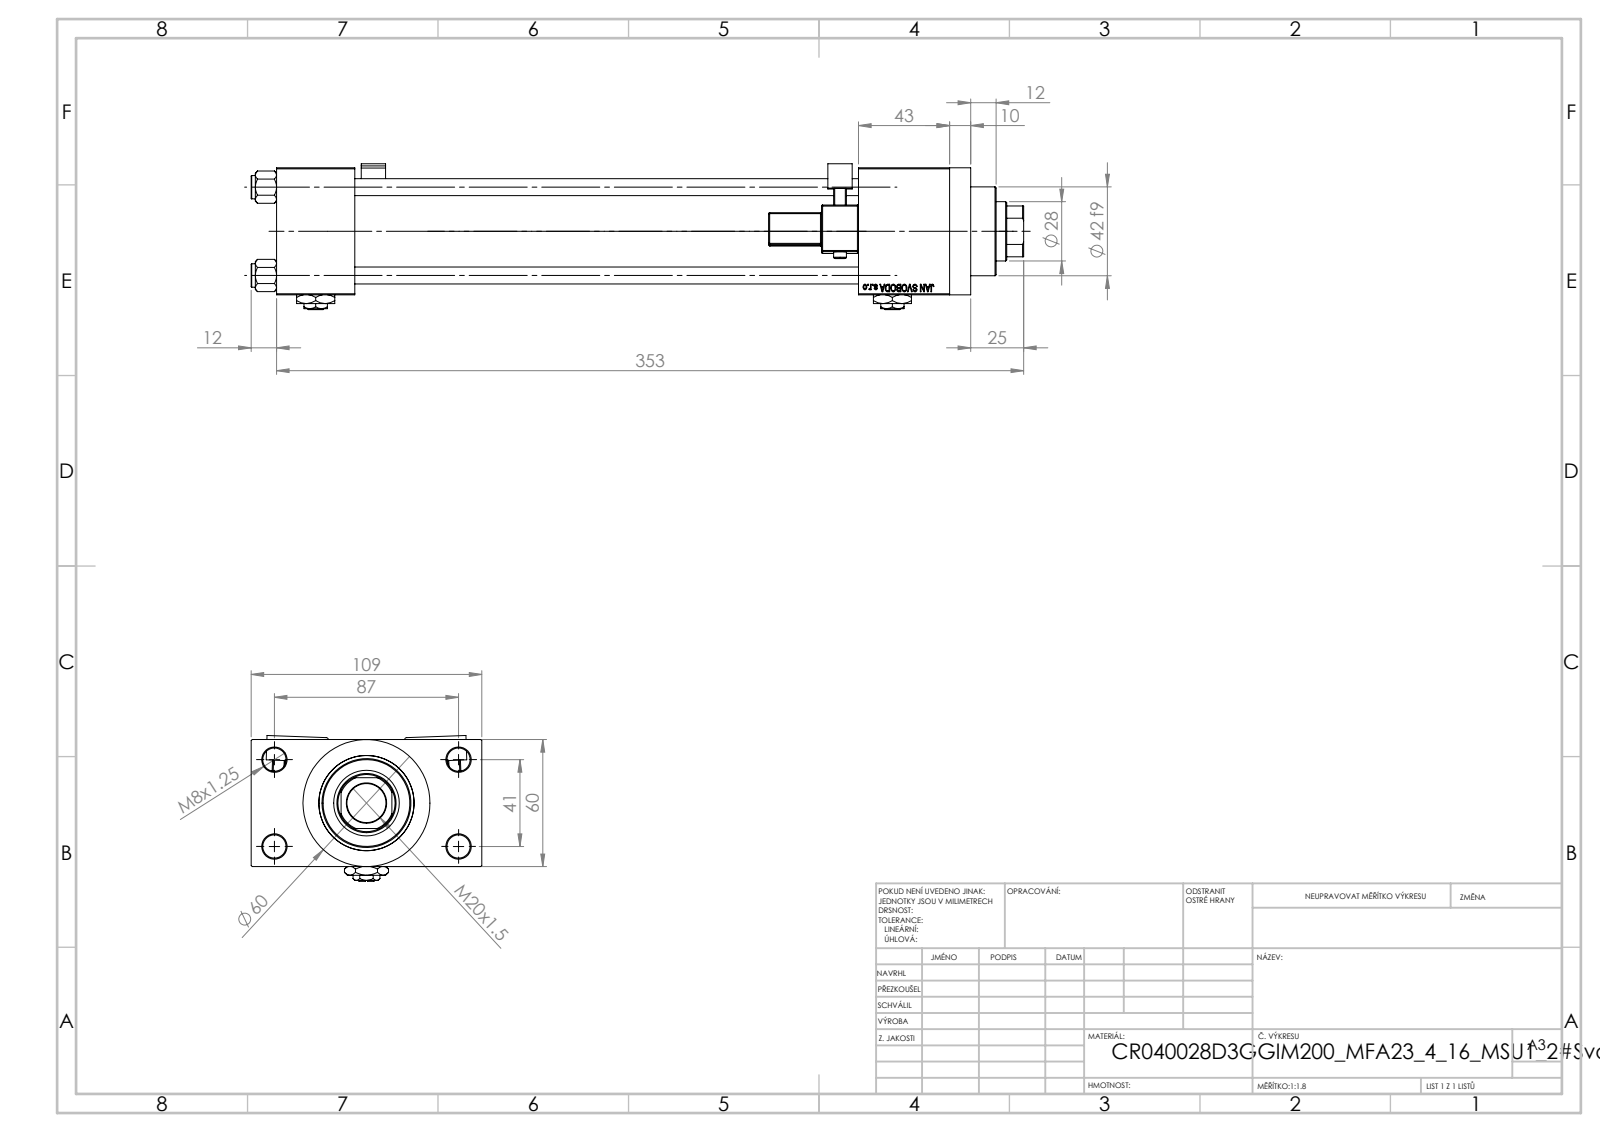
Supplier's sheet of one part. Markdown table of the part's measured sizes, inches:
| quantity | value |
| --- | --- |
| part name | V215CR_VCP_D; NUT_M5_D; V215_VC_A; V215CR_MSU (+3 more) |
| STEP written by | SolidWorks 2019 (CONFIG_CONTROL_DESIGN) |
| units | inches |
| bodies | 15 solids, 1360 faces (604 planar, 160 cylindrical, 596 other) |
| overall size | 14.37 × 4.291 × 2.713 |
| volume | 48.38 in³ |
| surface area | 348.9 in² |
| round holes (diameter × count) | 0.315 × 4, 0.433 × 4, 0.276 × 2, 0.656 × 2, 0.945 × 2, 0.728 × 1, 1.102 × 1, 1.22 × 1, 1.575 × 1, 1.772 × 1 |
| round bosses / shafts (diameter × count) | 0.433 × 4, 0.236 × 2, 2.362 × 1, 1.811 × 1, 1.654 × 1 |
| partial cylindrical surfaces (radius × count) | 0.02 × 48, 0.039 × 2, 0.098 × 2, 0.157 × 2, 0.531 × 1 |
| main face-to-face distances | 2.362, 9.37, 0.965, 3.327, 1.457, 10.827, 12.52, 11.063, 1.693, 4.291 |
| hole center spacings | 0.892, 1.161, 1.642, 1.856, 1.893, 2.533, 3.011, 1.614 |
